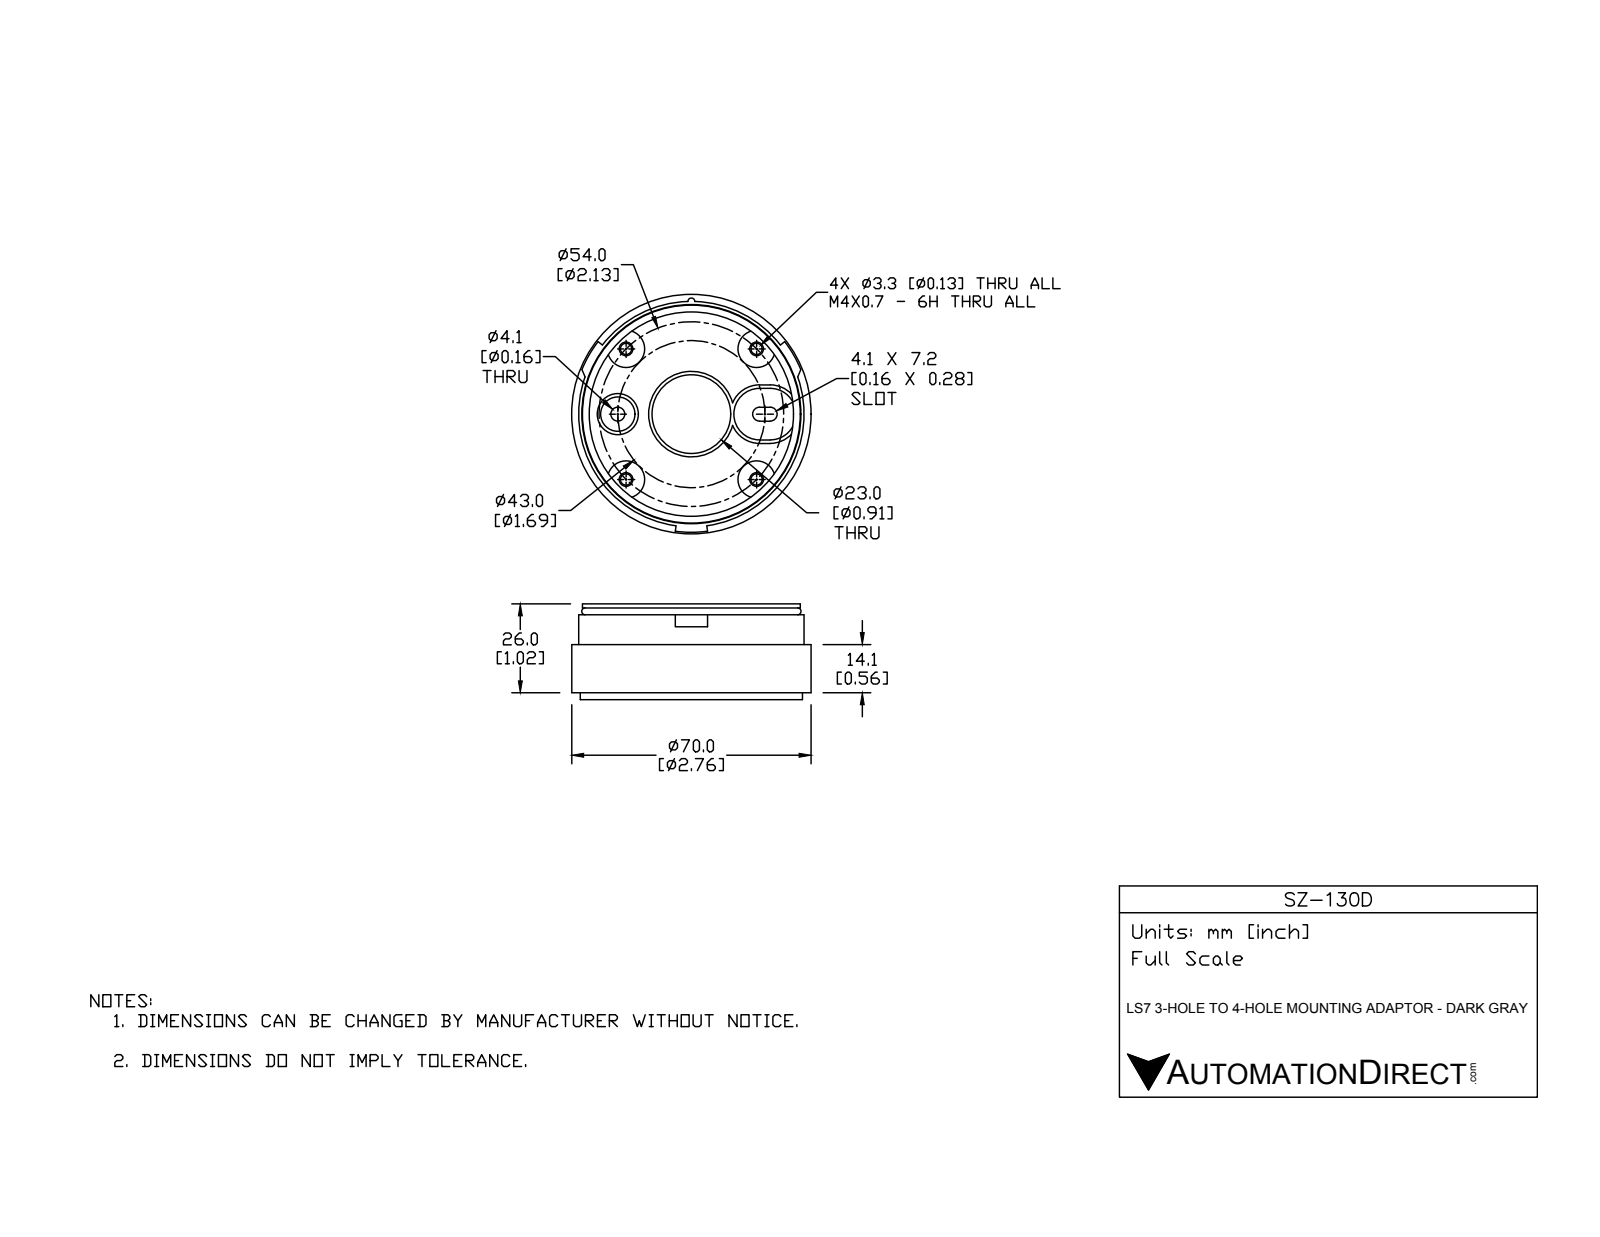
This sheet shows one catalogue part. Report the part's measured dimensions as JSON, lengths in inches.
{"part_name": "SZ-130D", "step_written_by": "SolidWorks 2016 (AUTOMOTIVE_DESIGN)", "units": "inches", "bodies": {"solids": 3, "faces": 132, "planar": 44, "cylindrical": 84, "other": 4}, "overall_size": [2.756, 2.756, 1.102], "volume_in3": 2.537, "surface_area_in2": 42.93, "round_holes": [[0.13, 4], [0.185, 4], [0.303, 4], [0.161, 1], [0.394, 1], [0.906, 1], [1.016, 1], [2.351, 1]], "round_bosses_or_shafts": [[0.264, 4], [2.756, 1], [2.594, 1], [2.559, 1], [2.508, 1], [2.366, 1], [0.984, 1], [0.472, 1]], "partial_cylinders_radius": [[0.166, 4], [0.214, 4], [0.081, 2], [0.297, 2], [0.337, 2], [0.039, 1], [1.36, 1]], "face_to_face_distances": [0.079, 0.281, 0.202, 0.976, 0.343, 0.353, 0.898, 0.695, 0.634, 0.555], "hole_center_spacings": [1.063, 1.503, 0.757, 1.766, 2.126, 0.846]}
